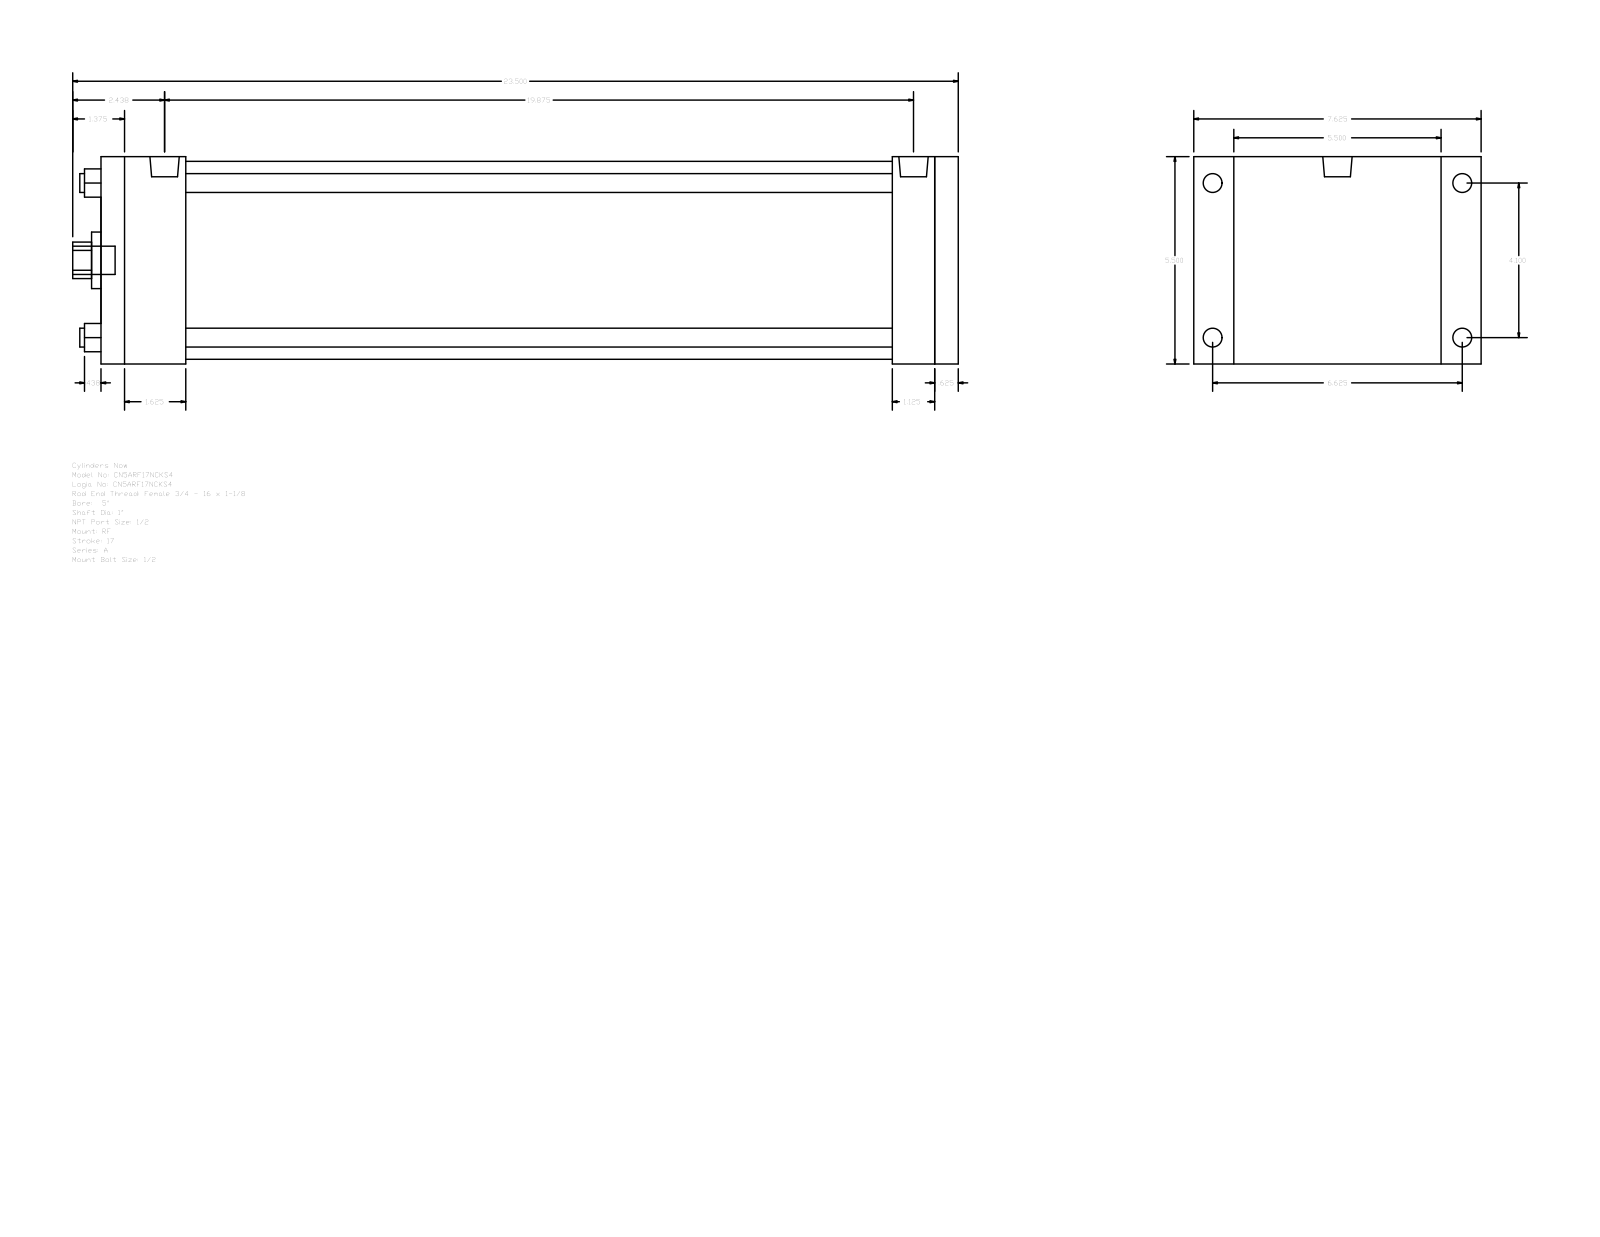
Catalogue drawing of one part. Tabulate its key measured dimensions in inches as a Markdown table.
| quantity | value |
| --- | --- |
| part name | A_RF__0500_1 |
| STEP written by | GSSL Pune (CONFIG_CONTROL_DESIGN) |
| units | inches |
| bodies | 0 solids, 92 faces (64 planar, 28 cylindrical, 0 other) |
| overall size | 23.5 × 7.625 × 5.5 |
| round holes (diameter × count) | 0.5 × 4, 1 × 1, 1.5 × 1, 5.25 × 1 |
| round bosses / shafts (diameter × count) | 0.5 × 4, 0.344 × 4, 0.778 × 2, 0.75 × 1 |
| partial cylindrical surfaces (radius × count) | 0.484 × 1 |
| main face-to-face distances | 5.5, 22.75, 22.125, 0.625, 1.125, 2.25, 19.875, 20.5, 21, 18.75 |
| hole center spacings | 2.899, 4.1, 5.798 |
